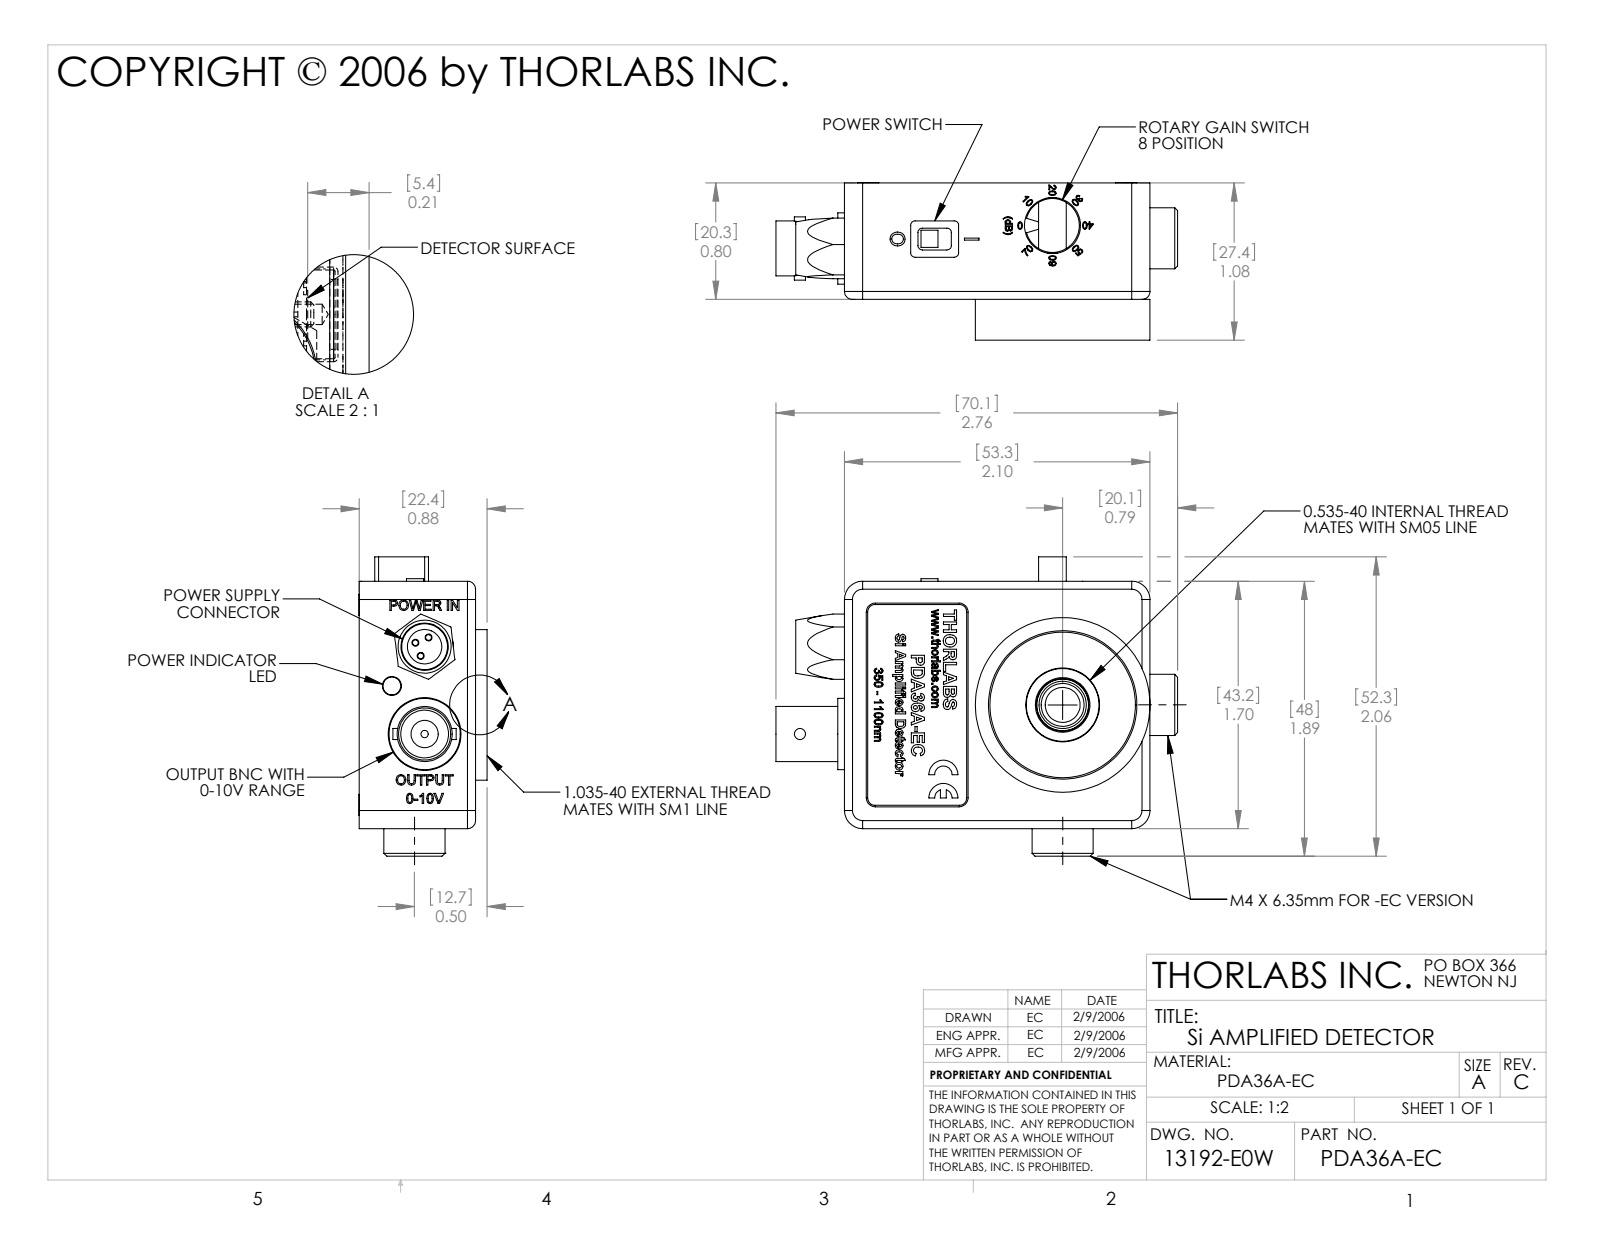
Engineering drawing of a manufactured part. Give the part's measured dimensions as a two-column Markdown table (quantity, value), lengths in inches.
| quantity | value |
| --- | --- |
| part name | 13192-E0W |
| STEP written by | SolidWorks 2011 (CONFIG_CONTROL_DESIGN) |
| units | inches |
| bodies | 0 solids, 529 faces (342 planar, 88 cylindrical, 99 other) |
| overall size | 2.761 × 2.058 × 1.082 |
| round holes (diameter × count) | 0.039 × 3, 0.13 × 2, 0.05 × 1, 0.13 × 1, 0.24 × 1, 0.315 × 1, 0.325 × 1, 0.328 × 1, 0.375 × 1, 0.385 × 1, 0.507 × 1, 1 × 1 |
| round bosses / shafts (diameter × count) | 0.147 × 4, 0.42 × 2, 1.2 × 1, 0.49 × 1, 0.378 × 1, 0.37 × 1, 0.236 × 1, 0.076 × 1 |
| partial cylindrical surfaces (radius × count) | 0.031 × 8, 0.095 × 8, 0.125 × 6, 0.055 × 4, 0.062 × 3, 0.05 × 2, 0.063 × 1, 0.075 × 1 |
| main face-to-face distances | 0.565, 0.063, 0.502, 0.502, 0.439, 0.063, 0.298, 0.8, 0.737, 0.235 |
| hole center spacings | 0.069, 0.098, 0.112, 0.138, 0.202, 0.212, 0.286, 0.339 |
